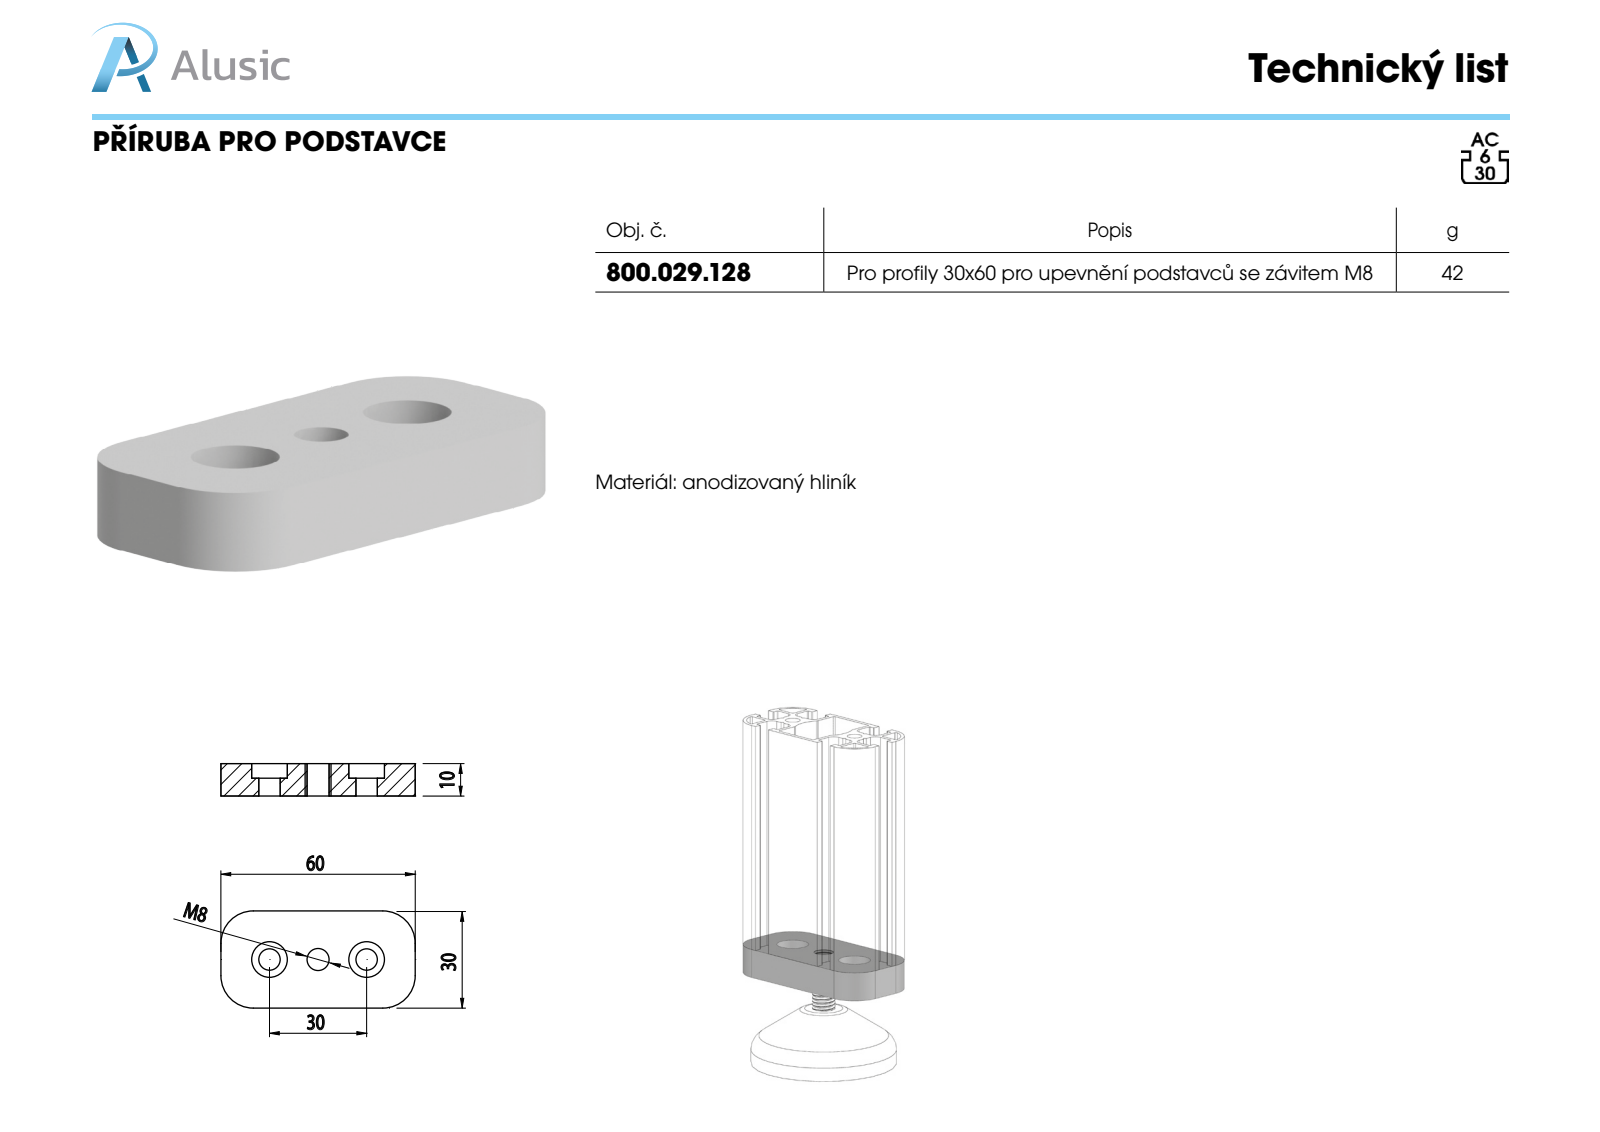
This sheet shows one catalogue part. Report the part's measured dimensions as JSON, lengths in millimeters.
{"part_name": "800.029.128", "step_written_by": "SolidWorks 2012 (CONFIG_CONTROL_DESIGN)", "units": "millimeters", "bodies": {"solids": 1, "faces": 22, "planar": 8, "cylindrical": 14, "other": 0}, "overall_size": [60, 30, 10], "volume_mm3": 15547, "surface_area_mm2": 5600, "round_holes": [[6.6, 2], [11, 2], [6.8, 1]], "partial_cylinders_radius": [[10, 4]], "face_to_face_distances": [10, 30, 5.5, 4.5, 60], "hole_center_spacings": [15, 30]}
